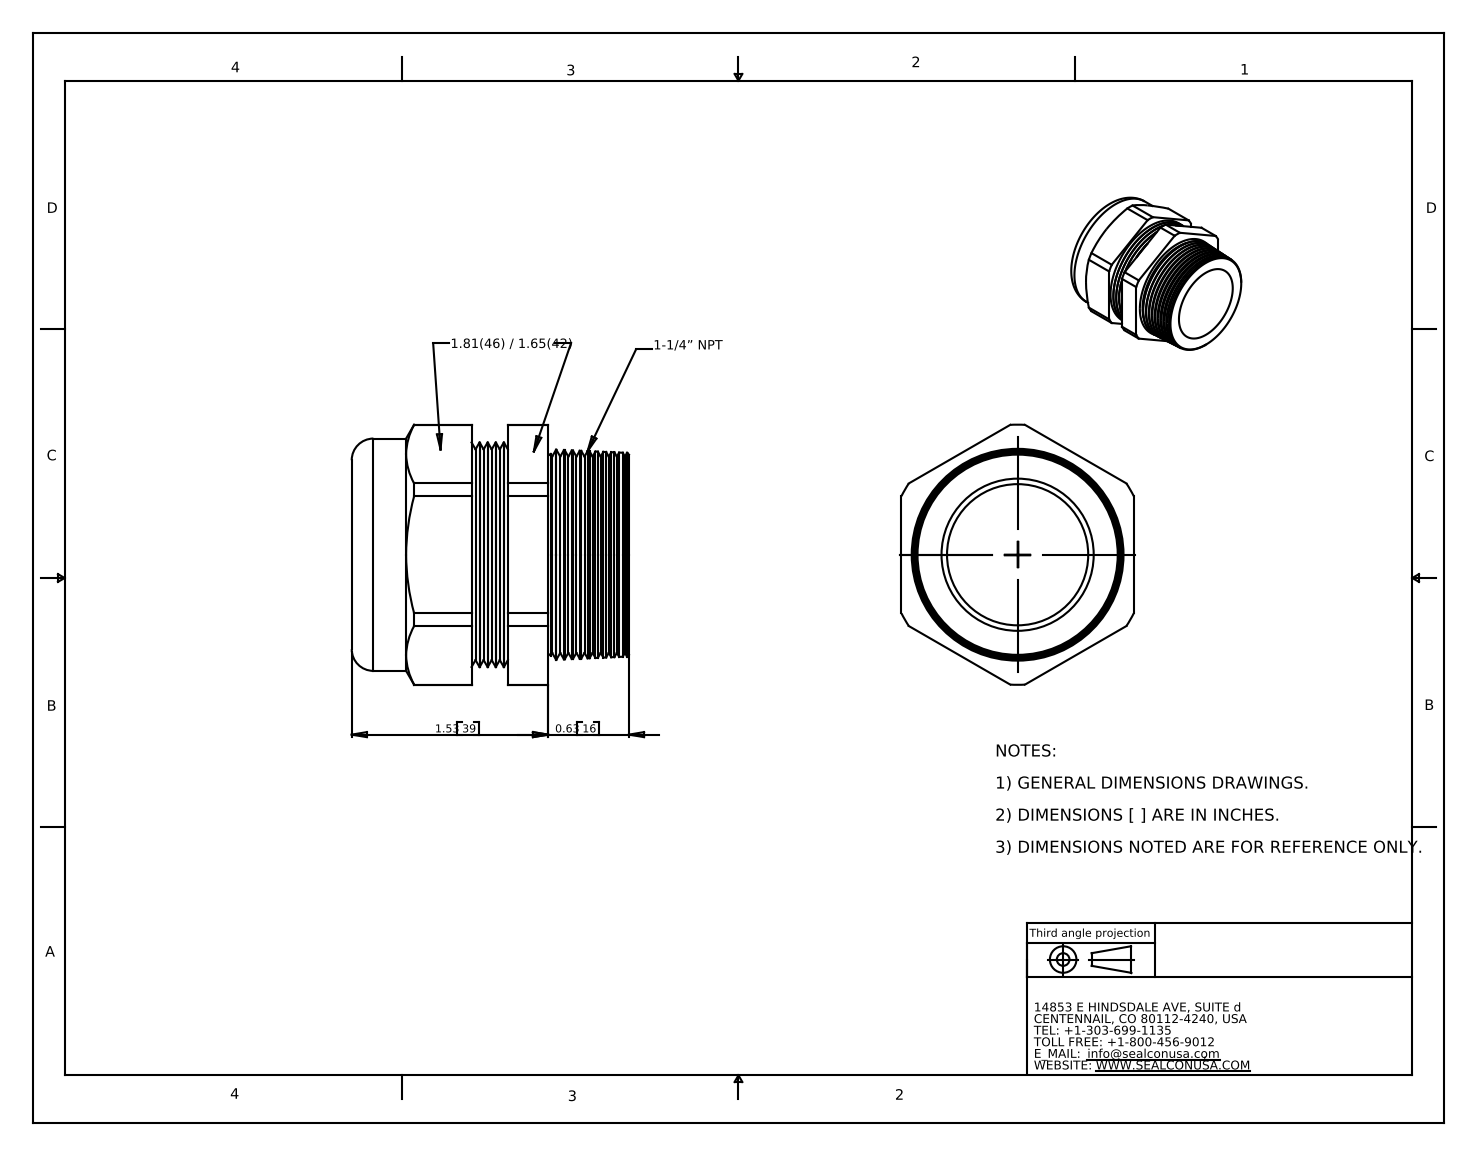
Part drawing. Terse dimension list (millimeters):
name: CD29LA-GY
written by: SolidWorks 2007 (CONFIG_CONTROL_DESIGN)
unit: mm
bodies: 2 solids, 150 faces (20 planar, 32 cylindrical, 98 other)
size: 54.9 × 51.5 × 46
volume: 50 540 mm³; area: 21 160 mm²
holes: 1× ⌀27.9, 1× ⌀35.4
bosses: 1× ⌀46, 1× ⌀44.4
rounds: 1× R25.8
face distances: 46, 44.1, 28.1, 16, 10.3, 38.4, 54.4, 30.4, 20.1, 8
